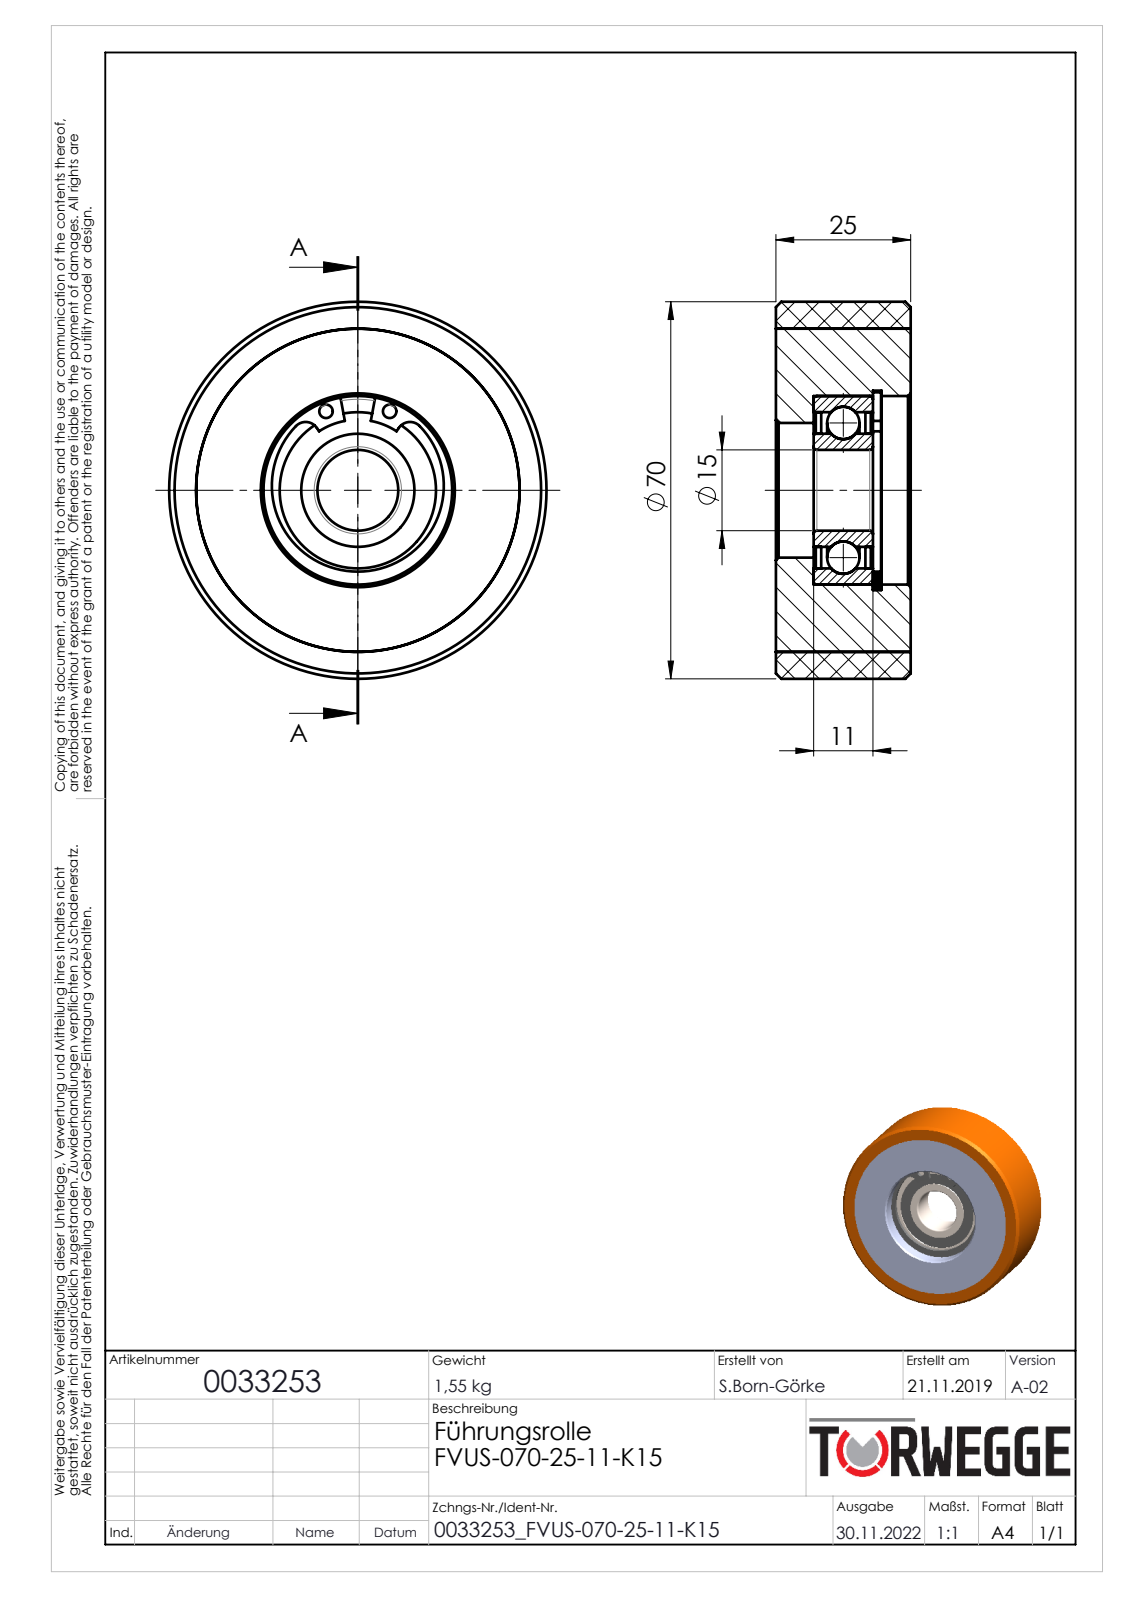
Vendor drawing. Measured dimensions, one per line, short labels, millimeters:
name: 0033253
written by: SolidWorks 2020 (AUTOMOTIVE_DESIGN)
unit: mm
bodies: 8 solids, 95 faces (21 planar, 48 cylindrical, 26 other)
size: 70 × 70 × 25
volume: 83 029 mm³; area: 32 494 mm²
holes: 2× ⌀2.5, 1× ⌀15, 1× ⌀21, 1× ⌀25, 1× ⌀29, 1× ⌀35, 1× ⌀60
bosses: 1× ⌀70, 1× ⌀37
rounds: 2× R2.5, 1× R13.1, 1× R15.95
face distances: 25, 7, 18, 11, 7.4, 17.6, 0.4, 10.6, 8.4, 16.6
hole spacings: 15.8, 11.8
